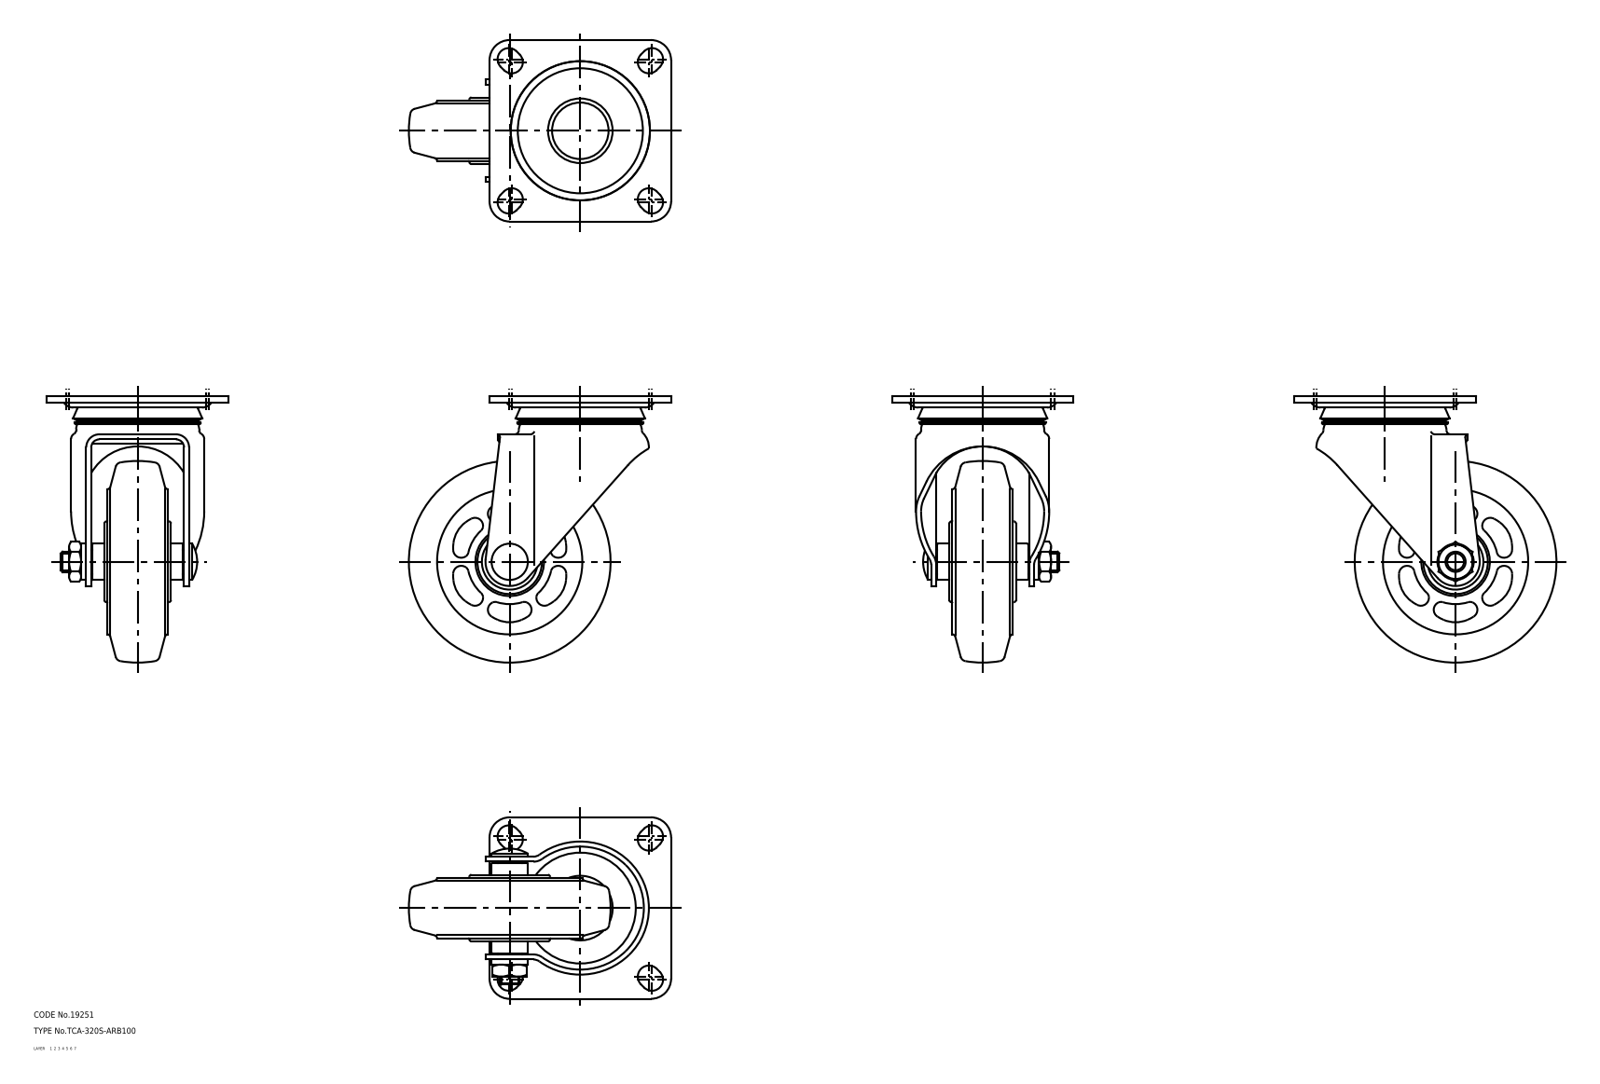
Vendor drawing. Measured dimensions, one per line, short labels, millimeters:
name: wheel; mounting plate; main shaft; axle (+1 more)
written by: CADfix (AUTOMOTIVE_DESIGN)
unit: mm
bodies: 5 solids, 271 faces (0 planar, 0 cylindrical, 271 other)
size: 132 × 130 × 90
volume: 278 718 mm³; area: 82 016 mm²
